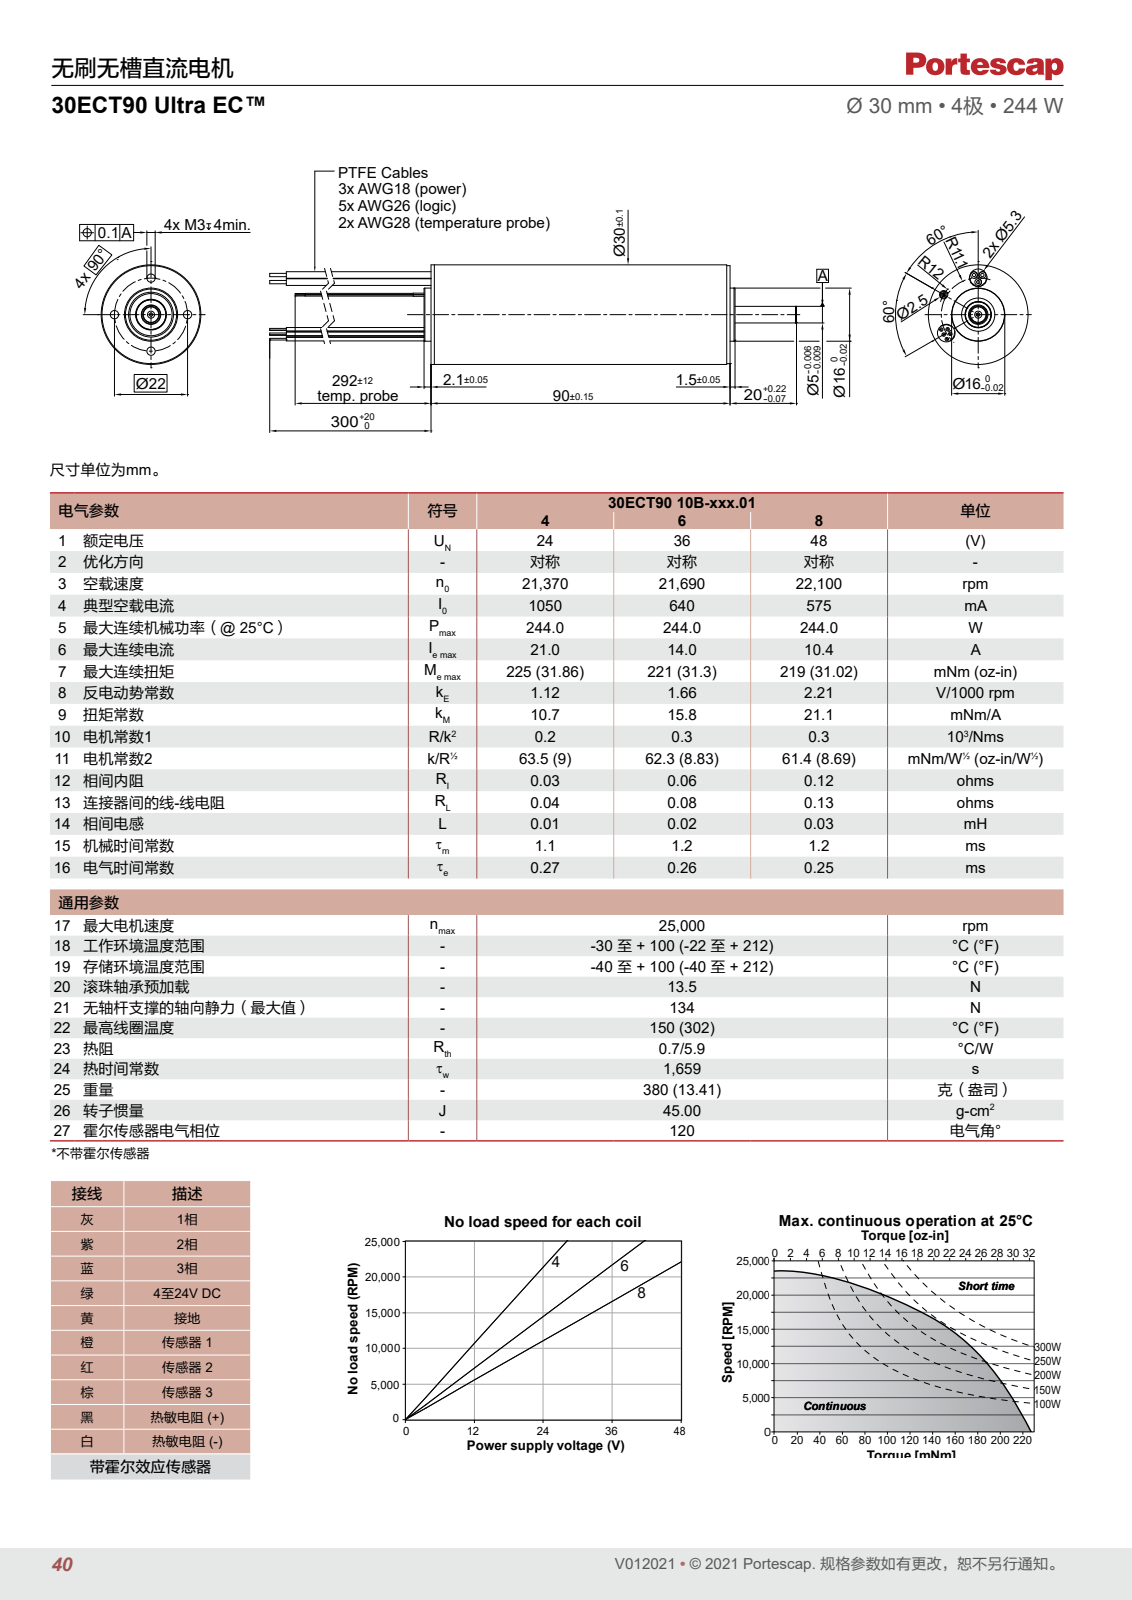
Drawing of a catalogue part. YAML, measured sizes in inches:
part_name: "30ECT_90"
step_written_by: "SolidWorks 2018 (AUTOMOTIVE_DESIGN)"
units: inches
bodies: {solids: 39, faces: 185, planar: 63, cylindrical: 56, other: 66}
overall_size: [16.142, 1.181, 1.181]
volume: 4.047
surface_area: 65.8
round_holes:
  - {diameter: 0.098, count: 5}
  - {diameter: 0.209, count: 2}
  - {diameter: 0.039, count: 1}
  - {diameter: 0.197, count: 1}
  - {diameter: 0.311, count: 1}
  - {diameter: 0.364, count: 1}
  - {diameter: 0.394, count: 1}
  - {diameter: 0.5, count: 1}
  - {diameter: 0.512, count: 1}
  - {diameter: 0.531, count: 1}
round_bosses_or_shafts:
  - {diameter: 0.02, count: 5}
  - {diameter: 0.079, count: 3}
  - {diameter: 0.039, count: 3}
  - {diameter: 0.018, count: 2}
  - {diameter: 0.013, count: 2}
  - {diameter: 0.01, count: 2}
  - {diameter: 1.181, count: 1}
  - {diameter: 1.161, count: 1}
face_to_face_distances: [3.154, 0.236, 3.39, 0.154, 3.307, 3.543, 0.055, 0.098, 3.209, 3.445]
hole_center_spacings: [0.433, 0.613, 0.437, 0.615, 0.866, 0.225, 0.237, 0.435]
